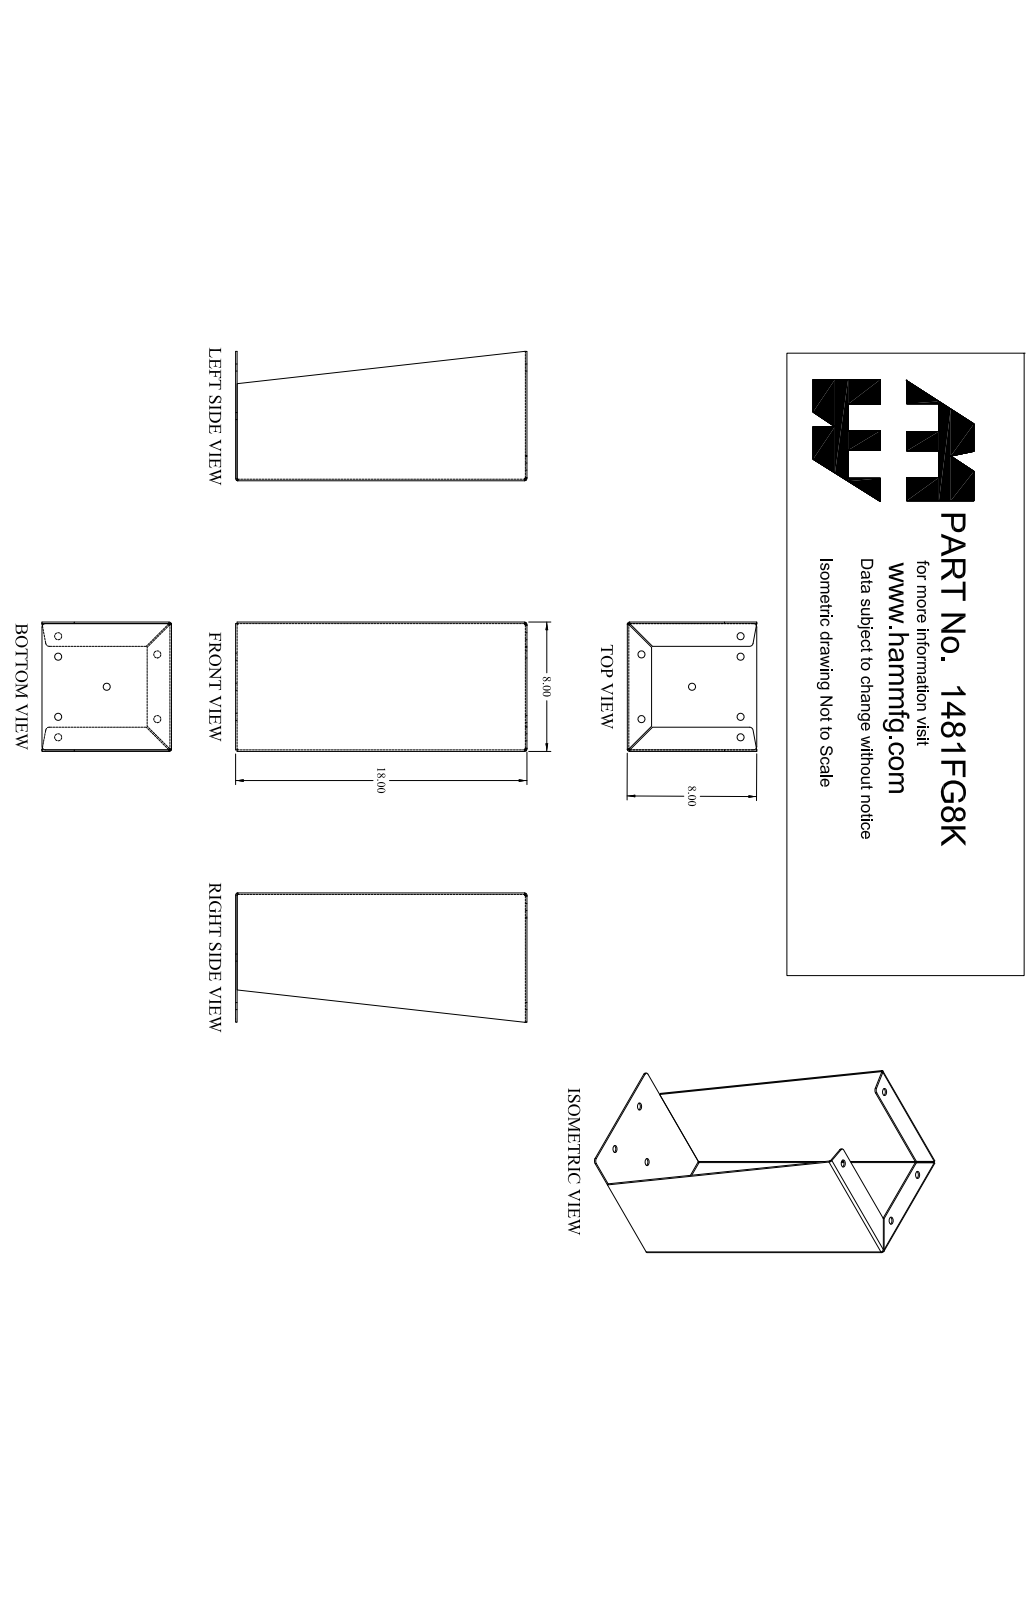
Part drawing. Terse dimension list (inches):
name: 1481FG8K_Default
written by: SolidWorks 2019 (CONFIG_CONTROL_DESIGN)
unit: in
bodies: 1 solid, 78 faces (42 planar, 30 cylindrical, 6 other)
size: 18 × 8 × 8
volume: 45.41 in³; area: 966.4 in²
holes: 7× ⌀0.437
rounds: 6× R0.048, 6× R0.143, 4× R0.22
face distances: 0.095, 7.905, 8, 7.81, 0.095, 17.81, 17.905, 17.905, 18, 7.905
hole spacings: 1.266, 3.529, 3.71, 4.332, 4.984, 6.126, 6.227, 7.239
